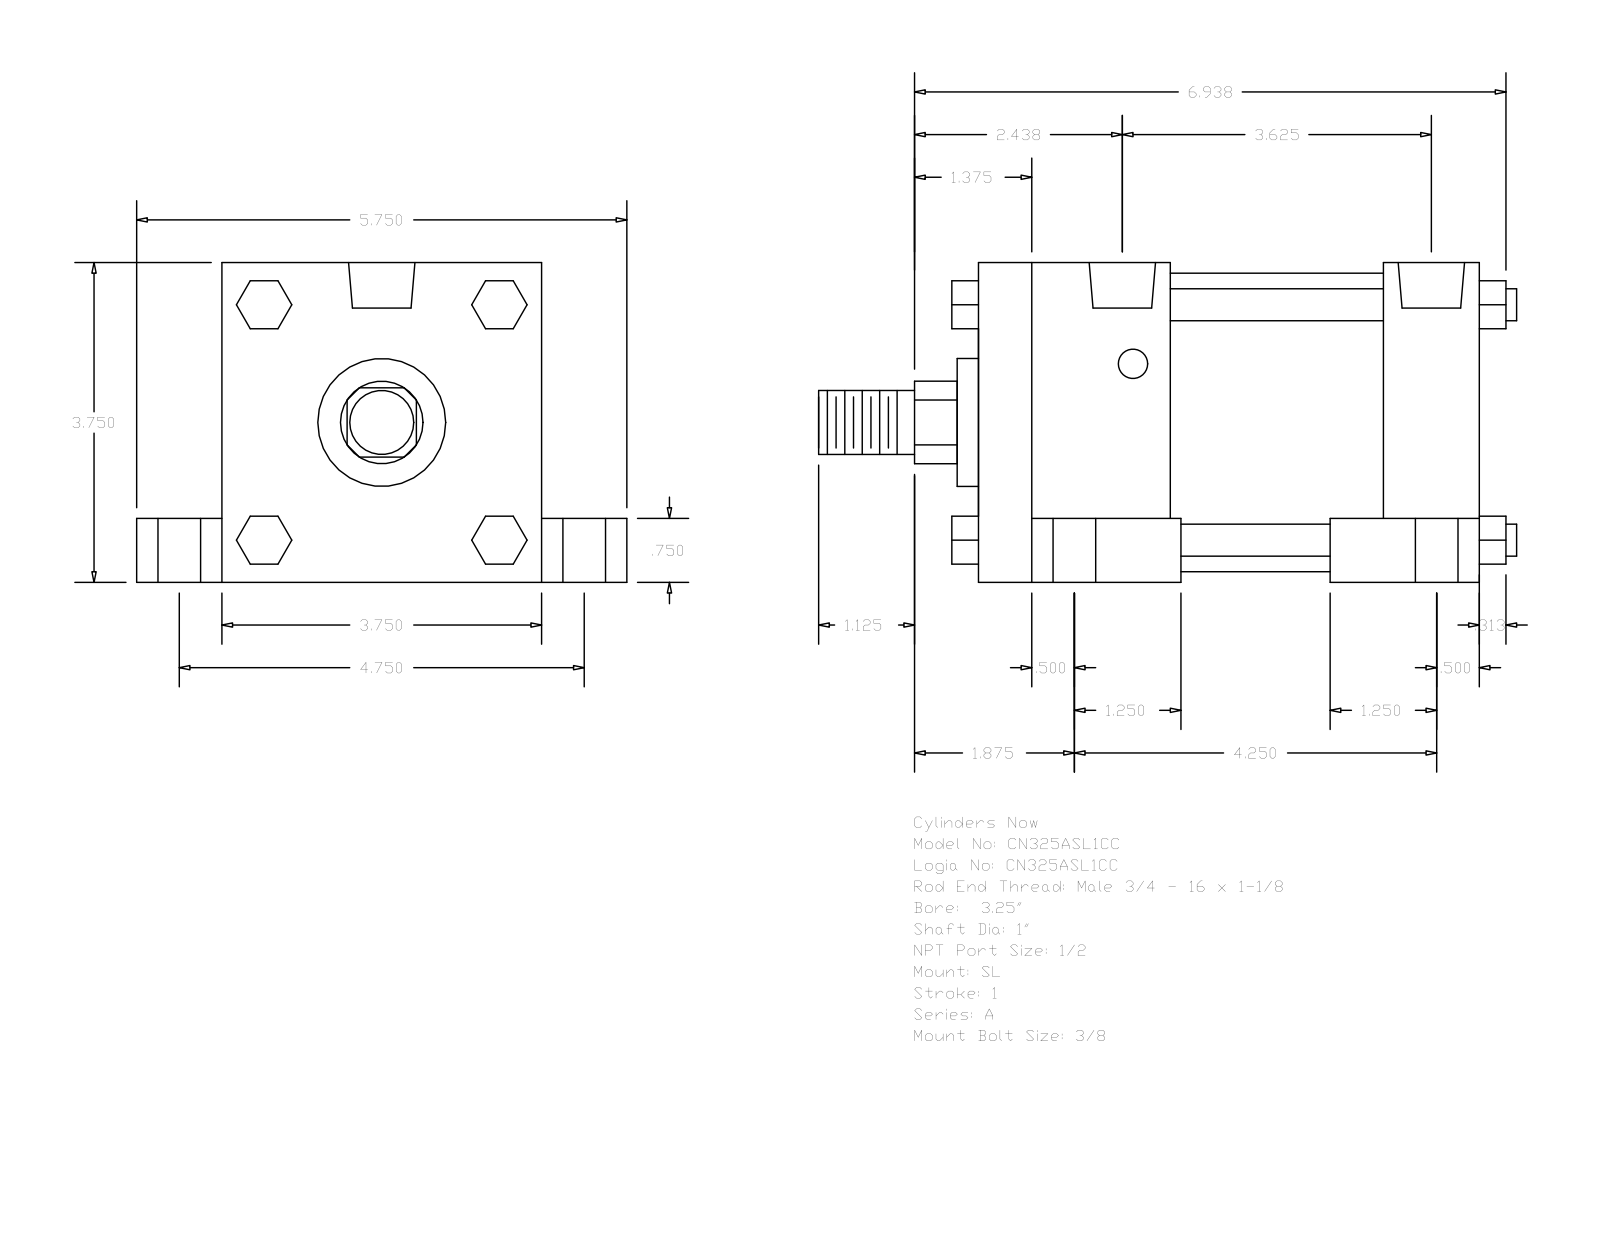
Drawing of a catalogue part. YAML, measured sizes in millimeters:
part_name: "A_SL__0325_1"
step_written_by: "GSSL Pune (CONFIG_CONTROL_DESIGN)"
units: millimeters
bodies: {solids: 0, faces: 150, planar: 114, cylindrical: 36, other: 0}
overall_size: [207.96, 146.05, 95.25]
round_holes:
  - {diameter: 8.73, count: 4}
  - {diameter: 12.7, count: 4}
  - {diameter: 19.05, count: 4}
  - {diameter: 19.77, count: 2}
round_bosses_or_shafts:
  - {diameter: 9.53, count: 4}
  - {diameter: 88.9, count: 1}
  - {diameter: 38.1, count: 1}
  - {diameter: 25.4, count: 1}
  - {diameter: 19.05, count: 1}
partial_cylinders:
  - {radius: 12.29, count: 1}
face_to_face_distances: [95.24, 149.23, 120.65, 19.05, 25.41, 76.19, 63.5, 57.15, 92.08, 28.58]
hole_center_spacings: [3.18, 60.35, 60.52, 62, 62.81, 85.72, 88.9, 107.95]
